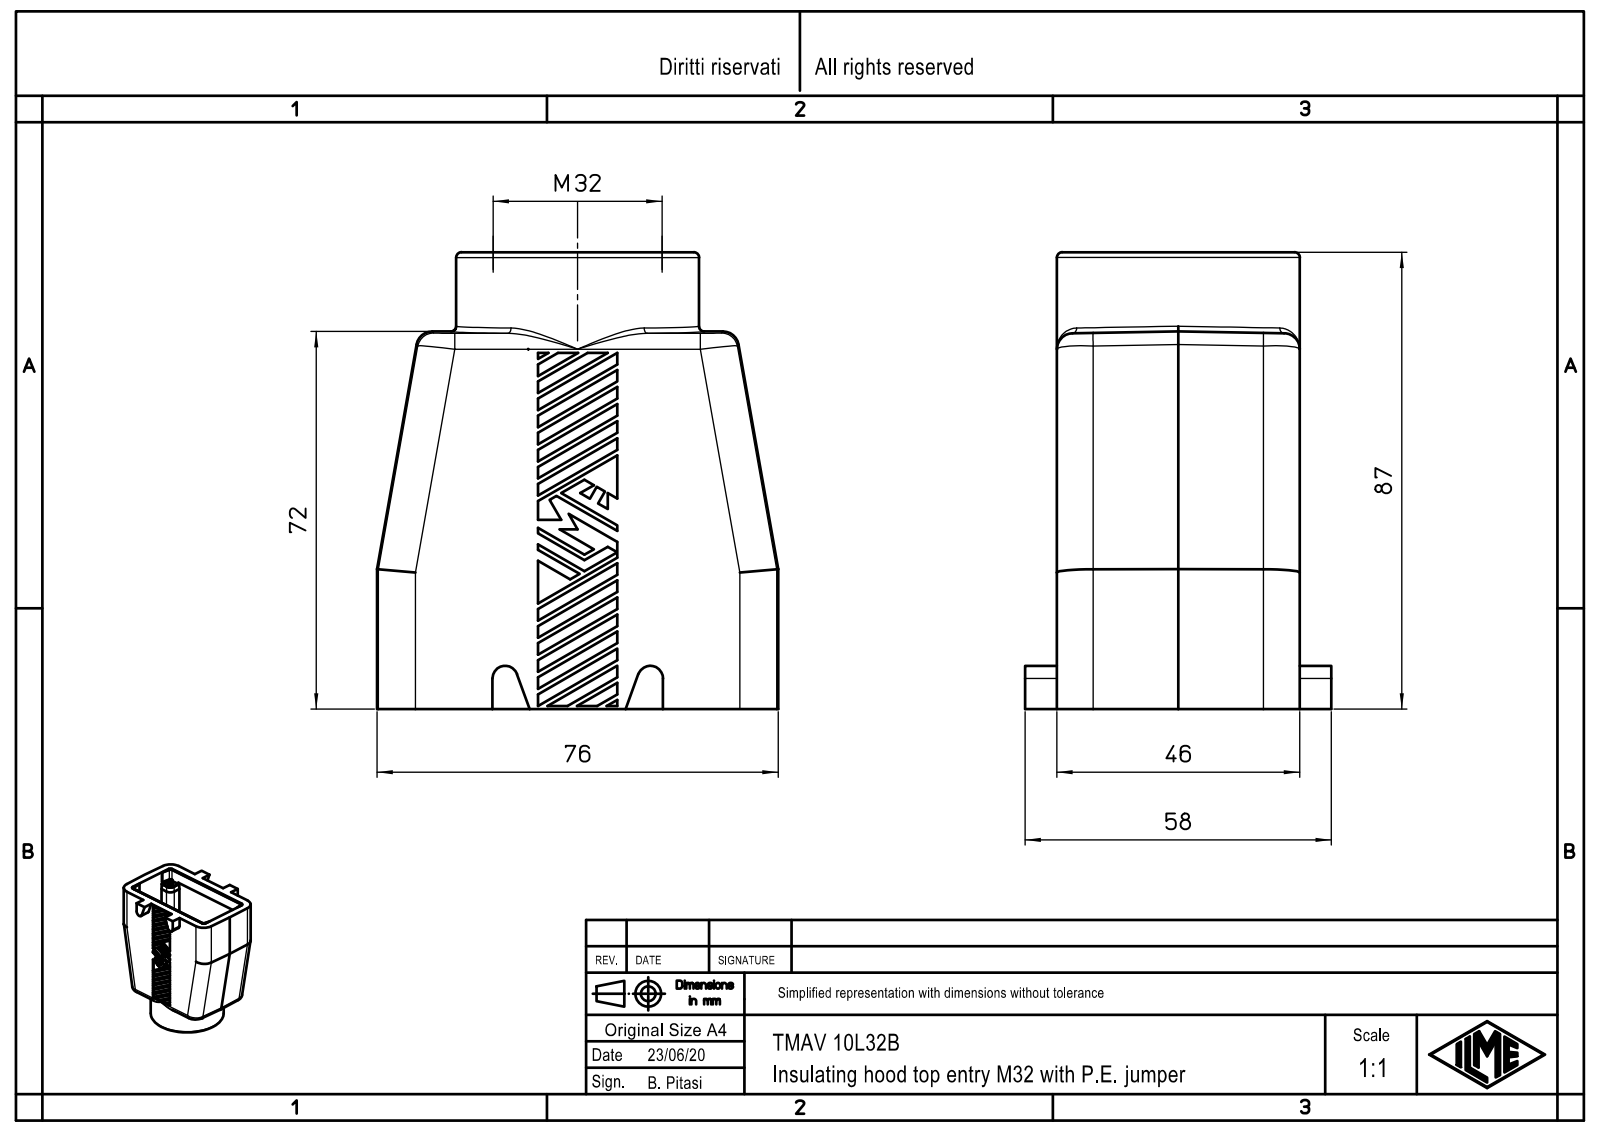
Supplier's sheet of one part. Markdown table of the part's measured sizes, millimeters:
| quantity | value |
| --- | --- |
| part name | TMAV_10.32B |
| STEP written by | Creo Elements/Direct Modeling 20.1B 02-Apr-2019 (C) Parametric Technology GmbH (AUTOMOTIVE_DESIGN) |
| units | millimeters |
| bodies | 1 solid, 568 faces (404 planar, 82 cylindrical, 82 other) |
| overall size | 86.49 × 76 × 58 |
| volume | 109 947 mm³ |
| surface area | 41 298 mm² |
| round holes (diameter × count) | 3 × 4, 3.5 × 4, 28 × 1, 32 × 1 |
| round bosses / shafts (diameter × count) | 4.8 × 4, 46 × 1 |
| partial cylindrical surfaces (radius × count) | 1.5 × 12, 7 × 8, 3 × 6, 1.3 × 4, 1.6 × 4, 2 × 4, 3.5 × 4, 2.4 × 2 |
| main face-to-face distances | 46, 45.5, 0.5, 65.99, 5.6, 5.3, 5.8, 40.2, 39.7, 6.1 |
| hole center spacings | 31.54, 27, 57, 63.07 |
